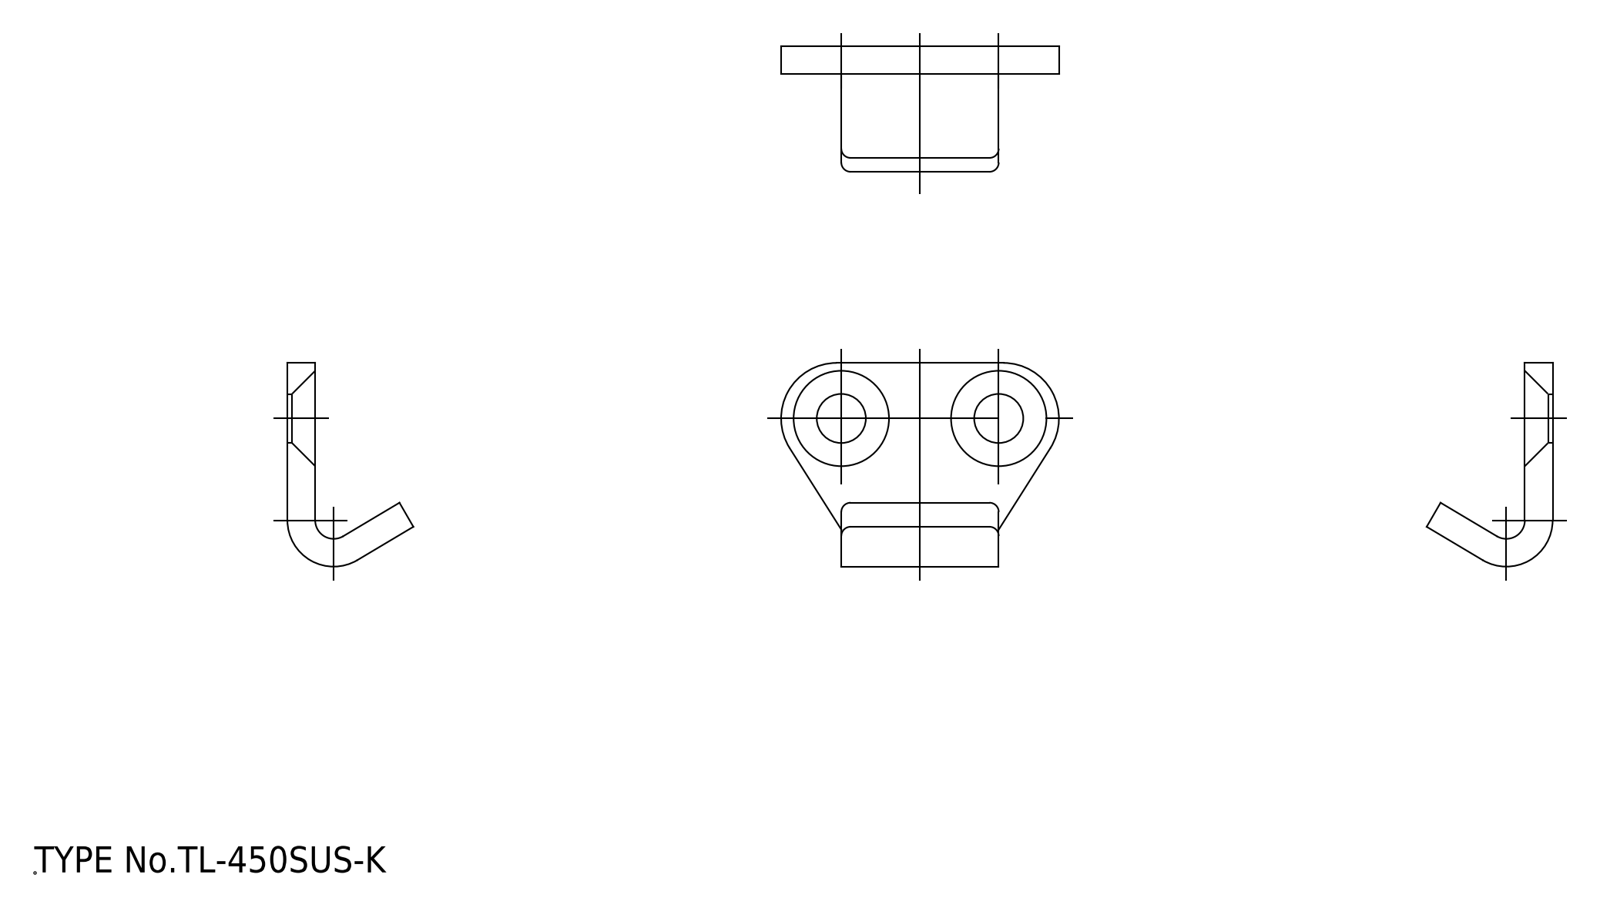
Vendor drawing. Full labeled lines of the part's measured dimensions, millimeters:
STEP written by: spGate 19.8.4 (****-****-****-****) (AUTOMOTIVE_DESIGN)
Units: millimetres
Bodies: 1 solid, 24 faces (12 planar, 8 cylindrical, 4 other)
Overall size (bounding box): 30 × 22 × 13.6
Volume: 1 787 mm³ · Surface area: 1 676 mm²
Round holes (diameter × count): ⌀5.3 ×2
Partial cylindrical surfaces — rounded edges, fillets, slot ends (radius × count): R6 ×2, R2 ×1, R5 ×1
Main face-to-face distances: 3, 2.99, 17
Hole centre spacings: 17
